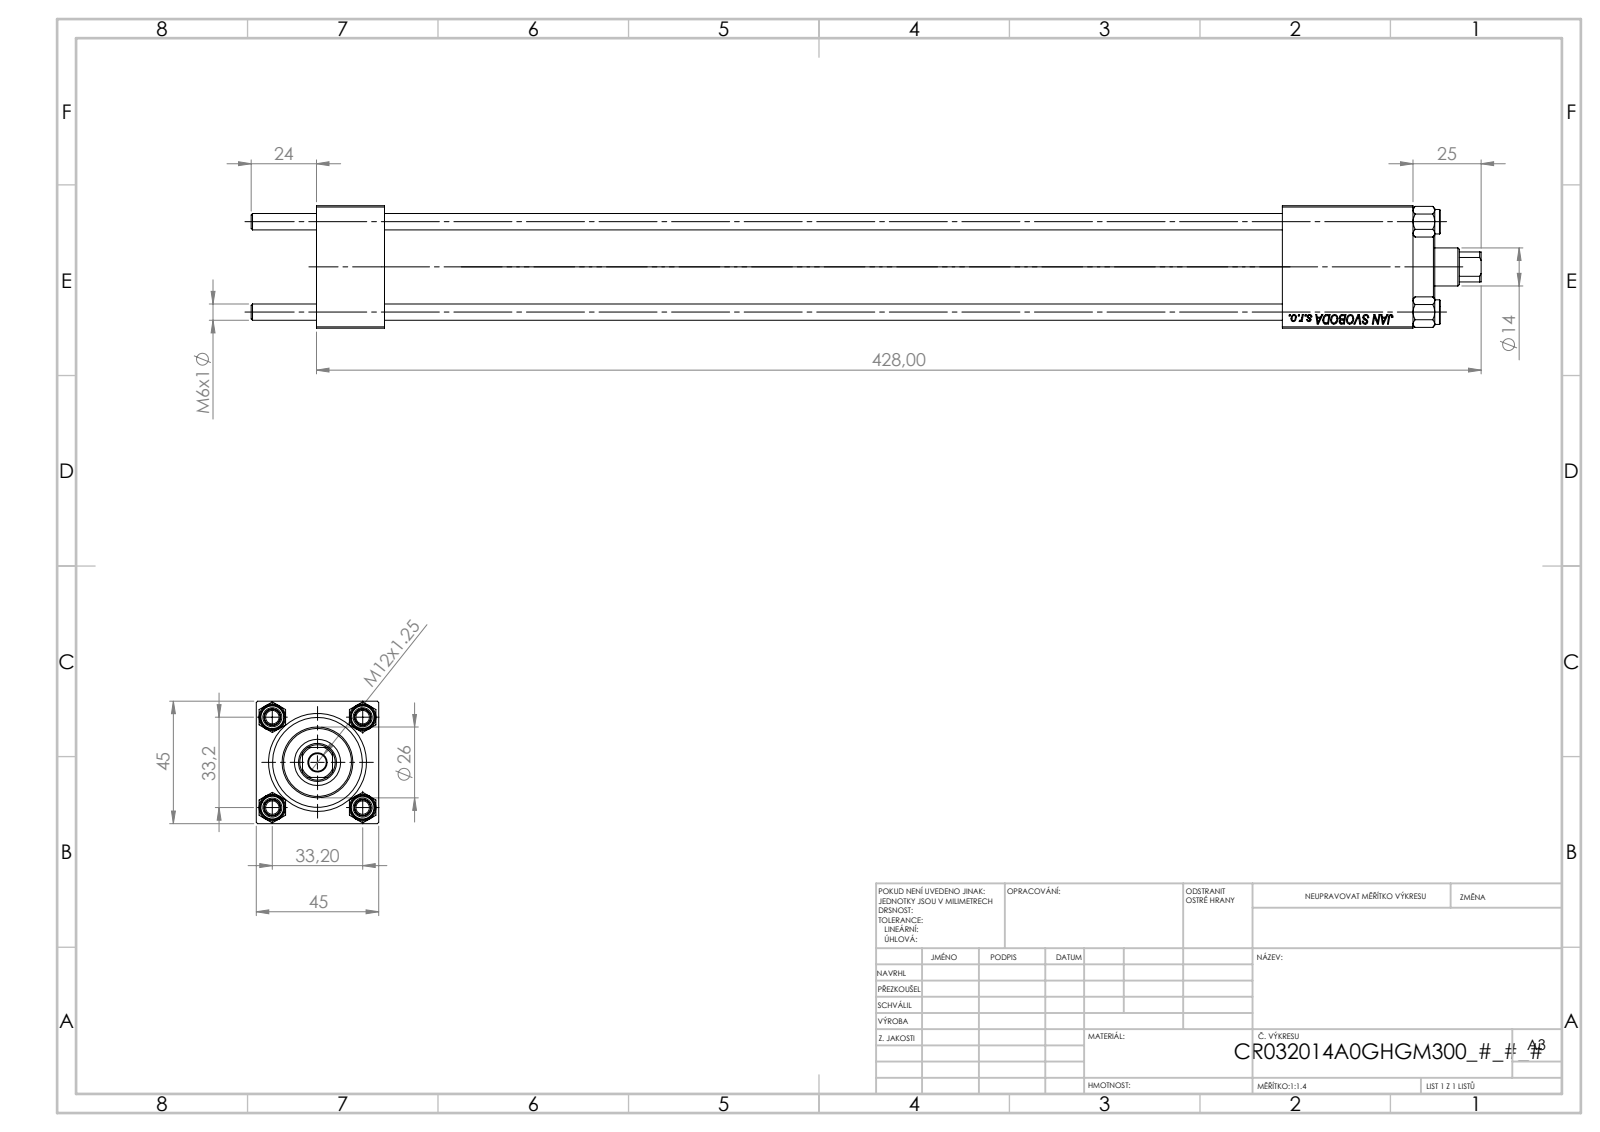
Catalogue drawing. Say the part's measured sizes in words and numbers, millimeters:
The part is named "NUT_M5; V215CR_VCP; V215_VC_A; V215CR_BODY_A (+1 more)". Its 3-D file was written by "SolidWorks 2019 (CONFIG_CONTROL_DESIGN)". It is 11 solids with 1133 faces: 519 planar, 78 cylindrical and 536 other. Overall it measures 452 by 45 by 45 millimeters. Its volume is 365 445 cubic millimeters and its surface area 167 826 square millimeters. Round holes: 4 of diameter 6, 2 of diameter 7, 2 of diameter 13.16, 2 of diameter 20, 1 of diameter 6.5, 1 of diameter 14, 1 of diameter 17, 1 of diameter 24, 1 of diameter 32, 1 of diameter 33. Round bosses or shafts: 4 of diameter 9, 1 of diameter 38, 1 of diameter 26. Partial cylindrical surfaces (rounded edges, fillets, slot ends): 1 of radius 6.5. The main face-to-face distances are 45, 25, 403, 378, 355, 330, 48, 374.3, 349.3, 19.3. The hole center spacings are 23.48, 33.2, 46.95, 355.5.
